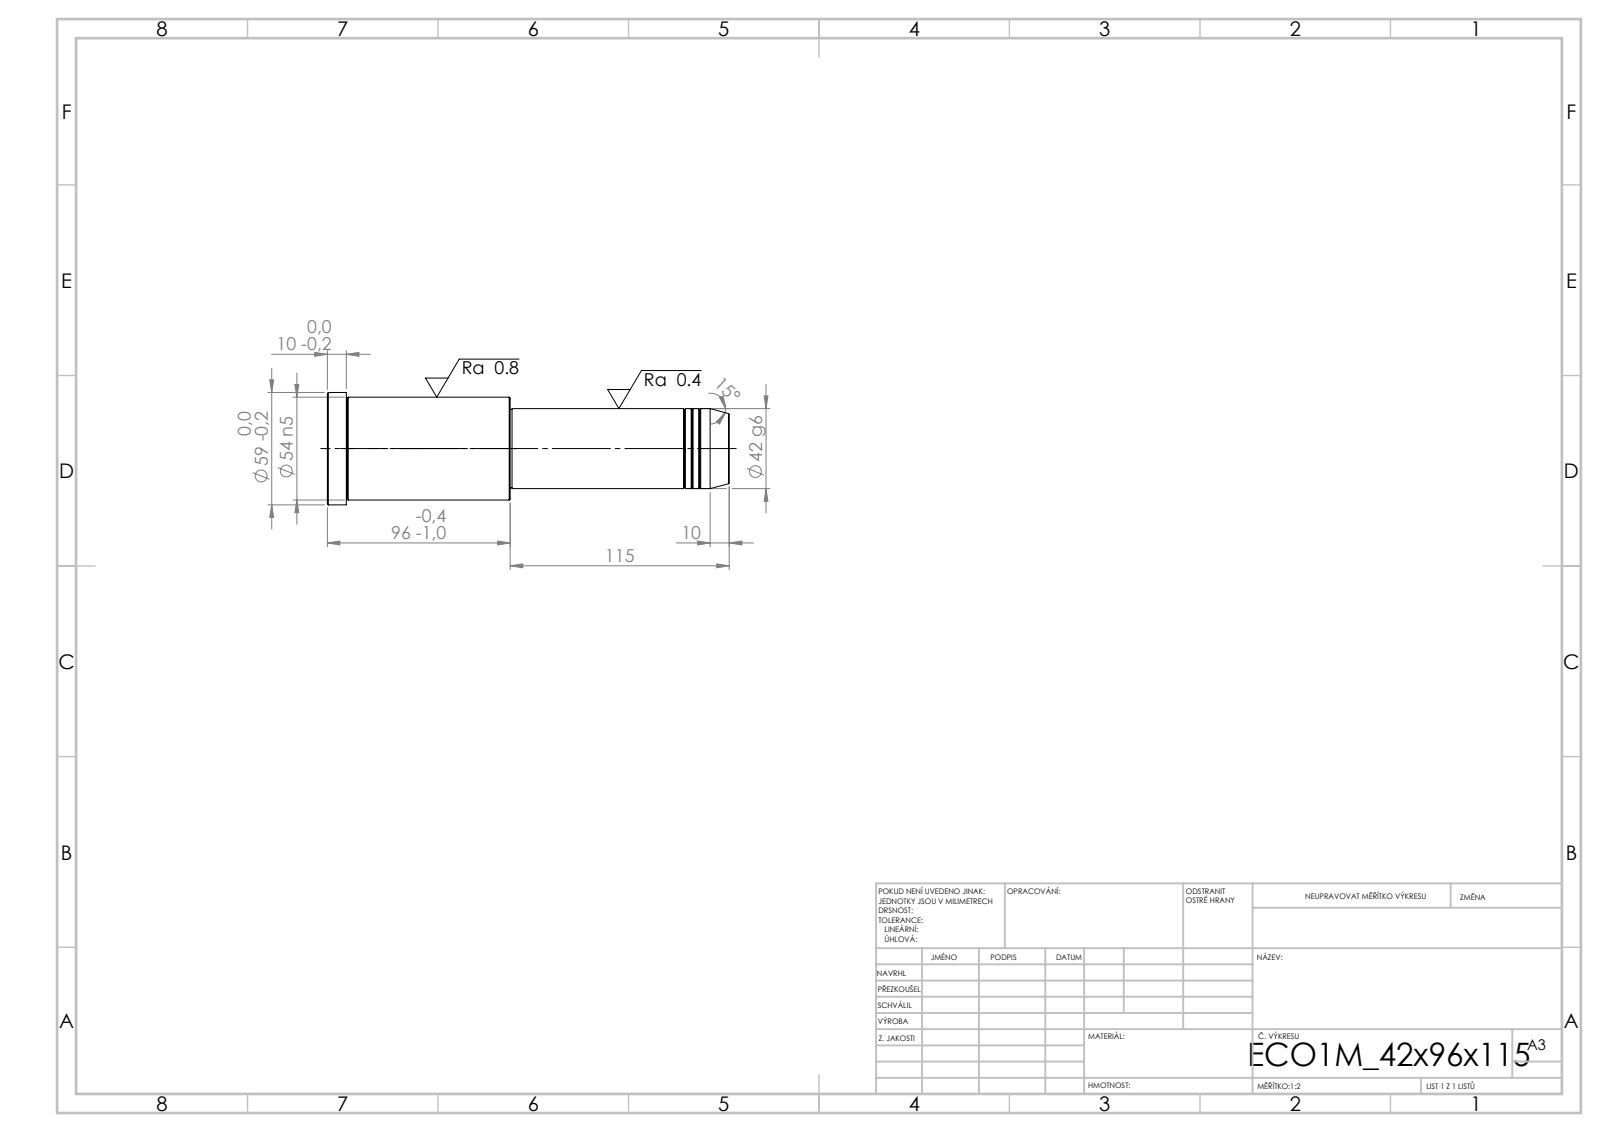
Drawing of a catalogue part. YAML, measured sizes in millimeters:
step_written_by: "SolidWorks 2019 (CONFIG_CONTROL_DESIGN)"
units: millimeters
bodies: {solids: 1, faces: 43, planar: 5, cylindrical: 14, other: 24}
overall_size: [211, 59, 59]
volume: 381600
surface_area: 37033
round_bosses_or_shafts:
  - {diameter: 59, count: 1}
  - {diameter: 54, count: 1}
  - {diameter: 42, count: 1}
  - {diameter: 41, count: 1}
face_to_face_distances: [211, 115, 96, 201, 86, 10, 114, 1, 87, 97]
